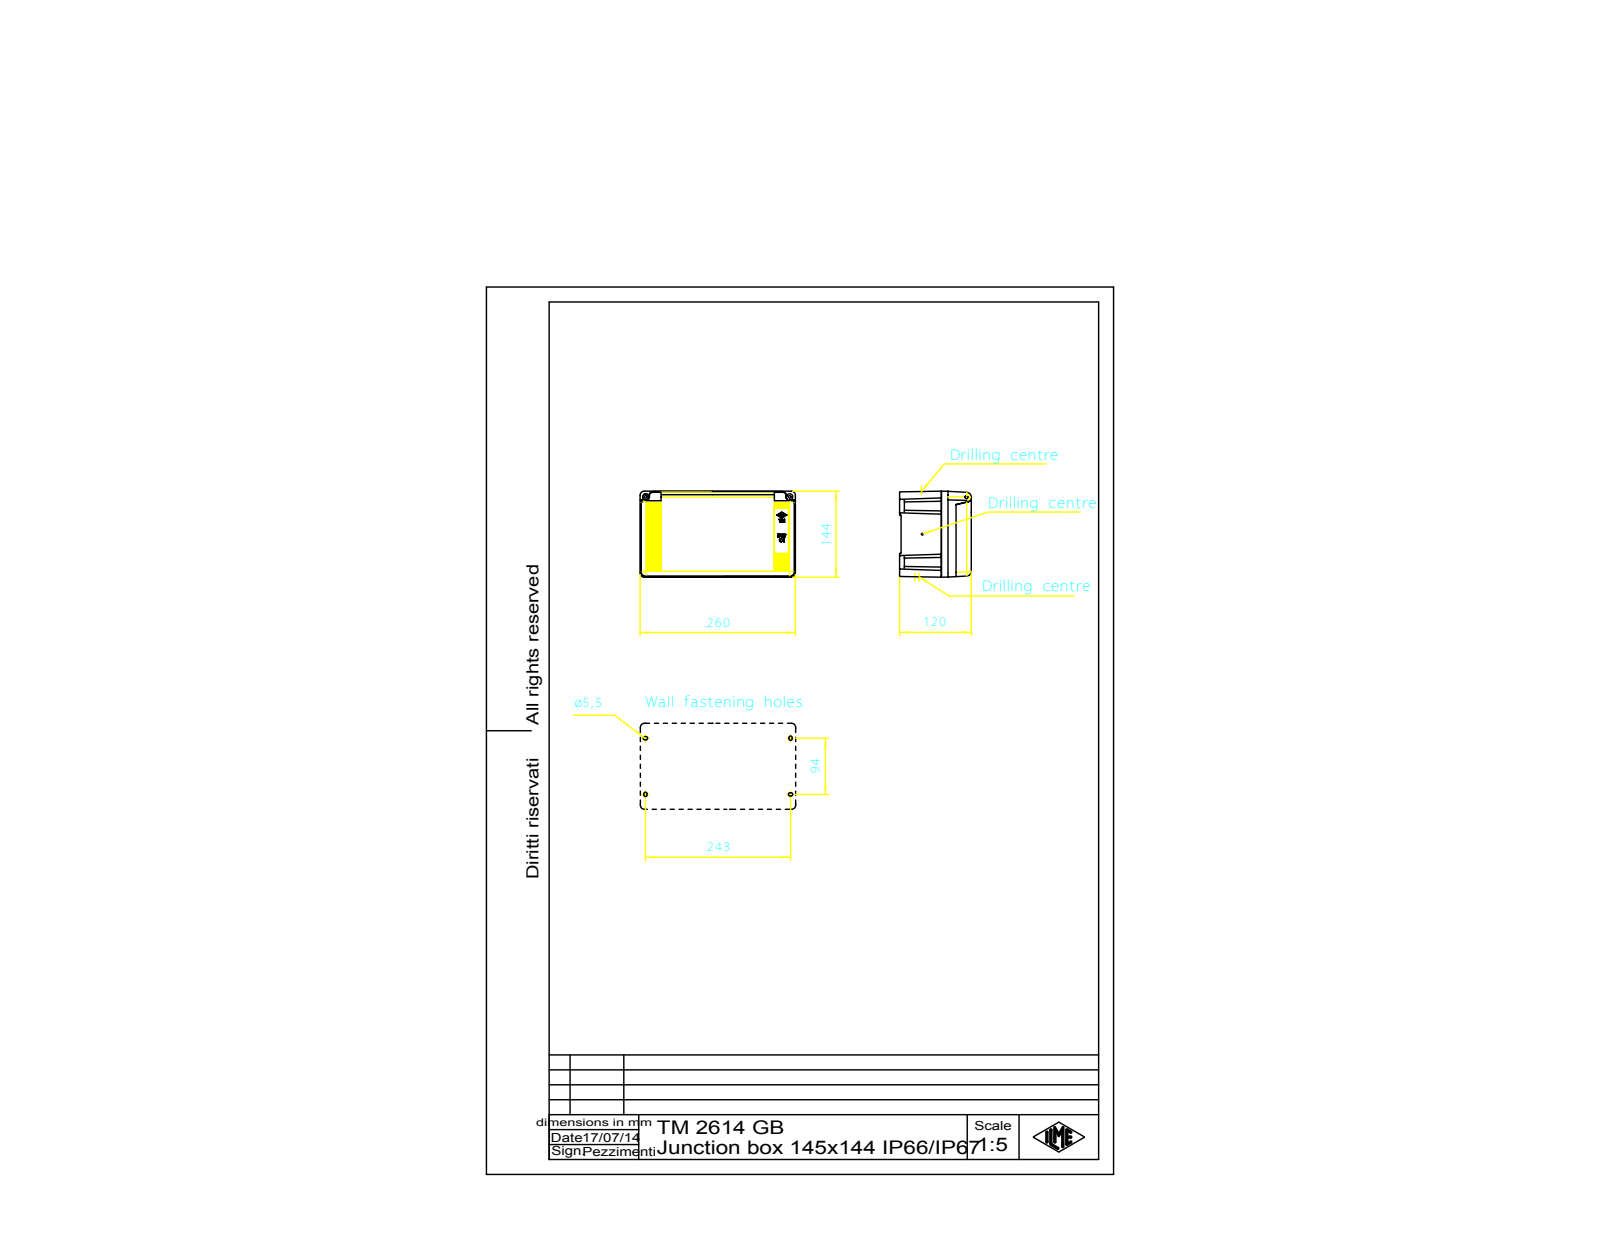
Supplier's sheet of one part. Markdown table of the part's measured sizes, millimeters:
| quantity | value |
| --- | --- |
| part name | SCATOLA_2614; SPORTELLO_2614; CALOTTA_2614; TM_2614_GB |
| STEP written by | Creo Elements/Direct Modeling 20.5B 27-May-2023 (C) Parametric Technology GmbH (AUTOMOTIVE_DESIGN) |
| units | millimeters |
| bodies | 3 solids, 1380 faces (1078 planar, 171 cylindrical, 131 other) |
| overall size | 260 × 144 × 120.4 |
| volume | 1 427 000 mm³ |
| surface area | 413 569 mm² |
| round holes (diameter × count) | 5.2 × 6, 5 × 1 |
| round bosses / shafts (diameter × count) | 8.5 × 6, 5 × 6, 6.7 × 2, 4 × 2 |
| partial cylindrical surfaces (radius × count) | 3.5 × 16, 7 × 12, 0.25 × 11, 3 × 10, 2.7 × 8, 8 × 8, 9.5 × 8, 0.5 × 5 |
| main face-to-face distances | 5, 112.5, 67.5, 45, 92, 87, 117.5, 25.5, 5.37, 19.5 |
| hole center spacings | 46.7, 123.21, 125, 195.78, 226.56, 241, 271.49, 150 |
